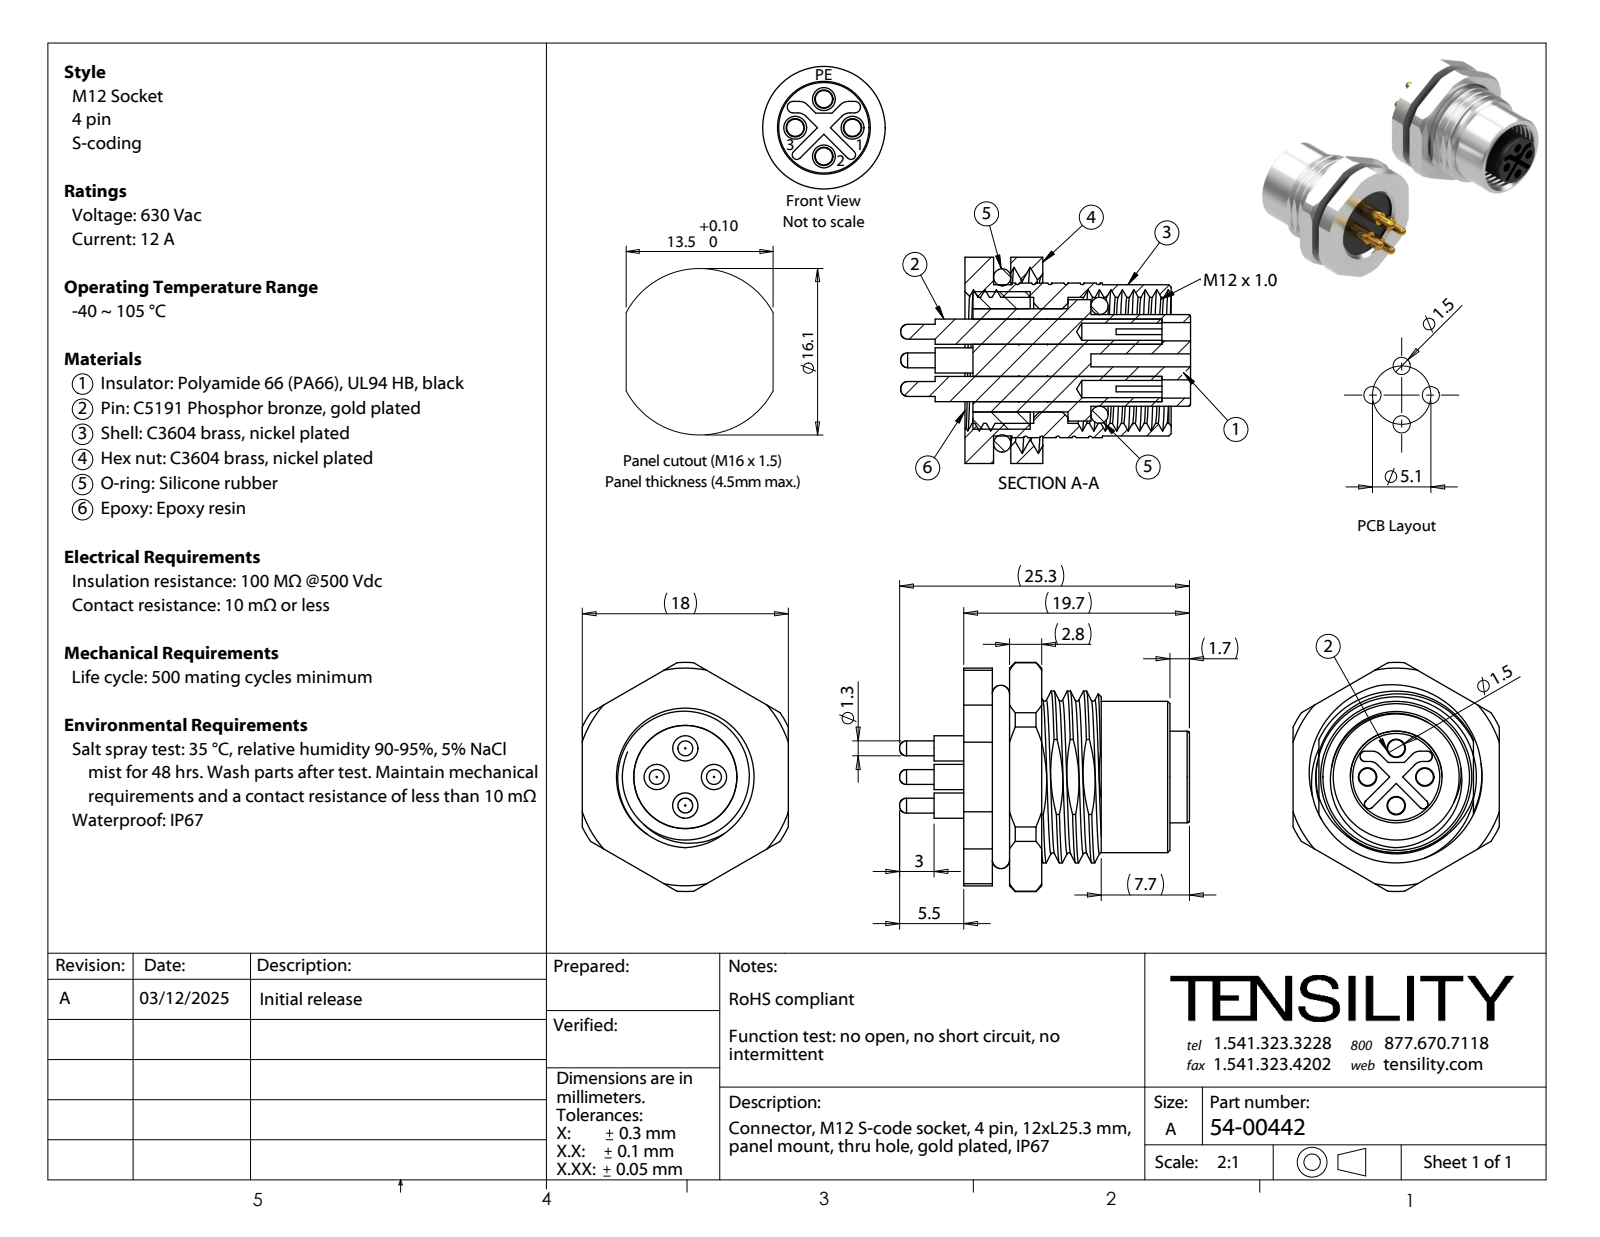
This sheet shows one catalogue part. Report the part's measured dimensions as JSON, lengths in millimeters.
{"part_name": "54-00442-06; 54-00442-03; 54-00442-05; 54-00442-02 (+3 more)", "step_written_by": "SolidWorks 2021 (CONFIG_CONTROL_DESIGN)", "units": "millimeters", "bodies": {"solids": 10, "faces": 328, "planar": 108, "cylindrical": 133, "other": 87}, "overall_size": [25.3, 19.8, 19.44], "volume_mm3": 2893, "surface_area_mm2": 5918, "round_holes": [[1.5, 4], [1.6, 4], [9, 1], [11, 1], [14, 1]], "round_bosses_or_shafts": [[2.2, 4], [1.3, 4], [13.2, 1], [12, 1], [10.6, 1], [8, 1]], "partial_cylinders_radius": [[1, 4], [0.4, 2], [0.45, 2], [7.5, 1], [9.5, 1], [10, 1]], "face_to_face_distances": [2.5, 3.3, 18, 5, 0.7, 1.8, 0.8, 4, 4.3, 1.5], "hole_center_spacings": [2.5, 3.54, 5]}
